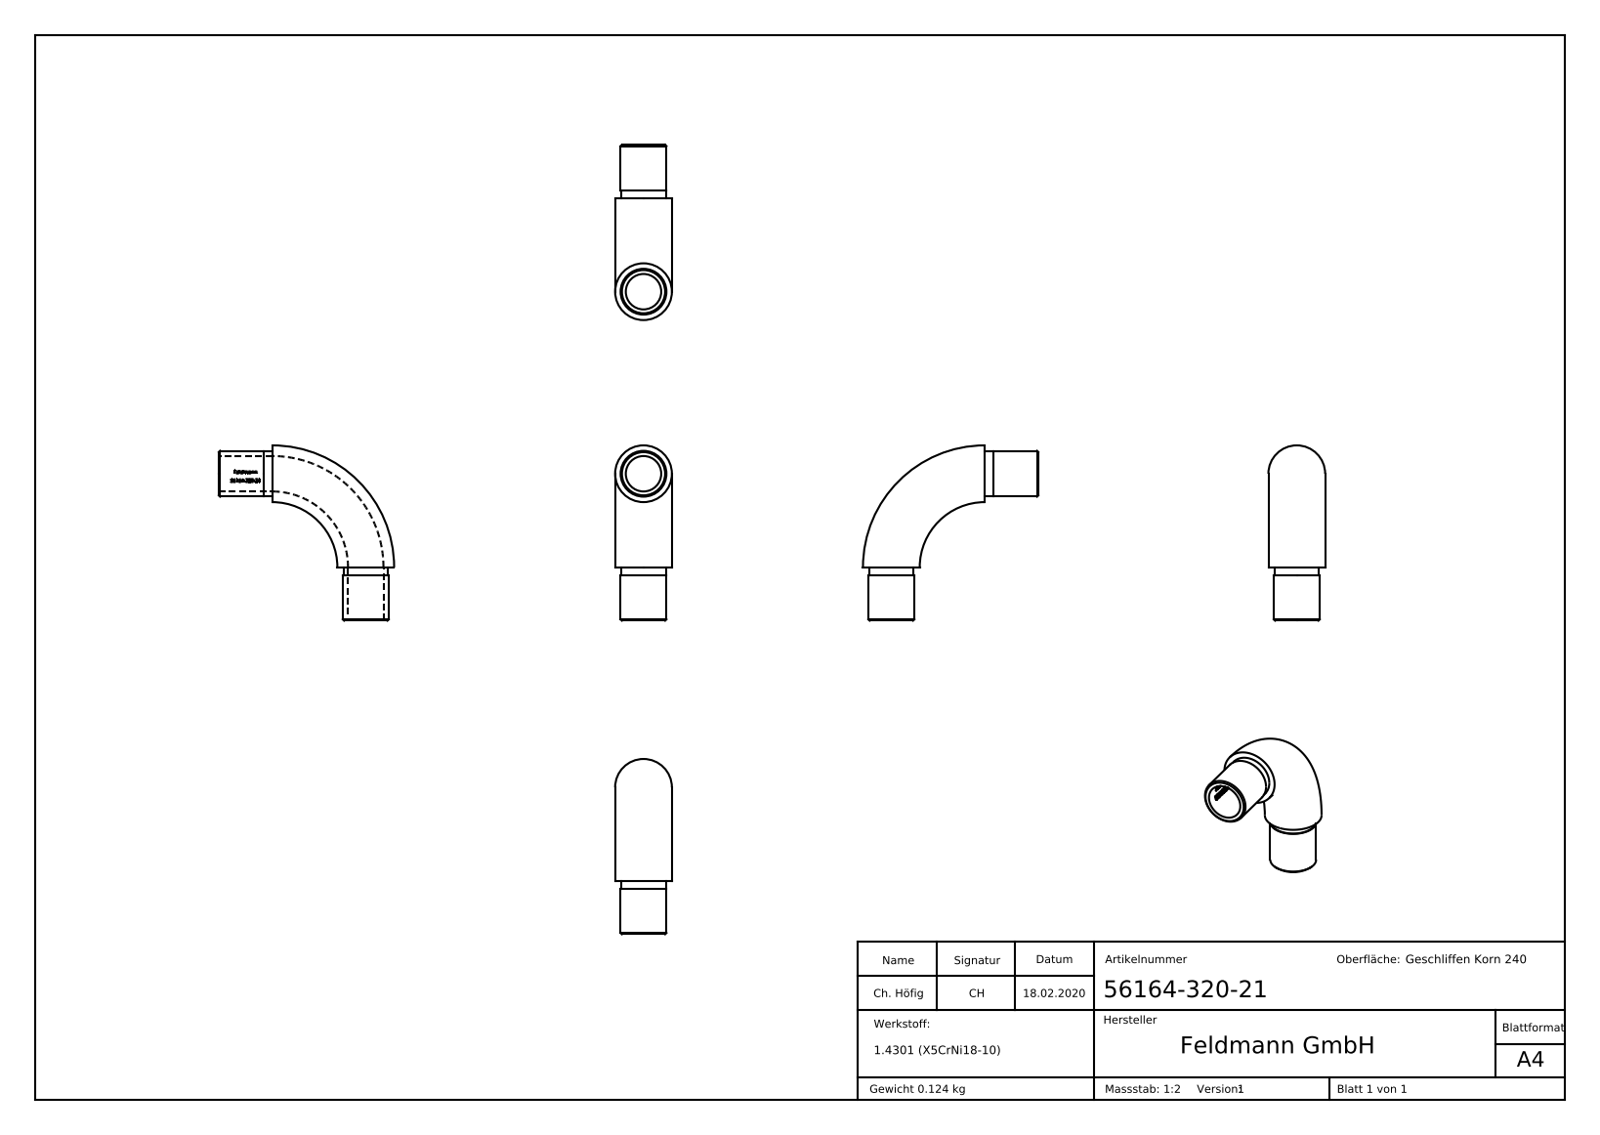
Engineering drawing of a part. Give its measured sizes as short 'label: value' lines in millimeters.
name: 56164-320-21
written by: SolidWorks 2015 (CONFIG_CONTROL_DESIGN)
unit: mm
bodies: 1 solid, 266 faces (120 planar, 33 cylindrical, 113 other)
size: 65.8 × 65.8 × 21.3
volume: 15 662 mm³; area: 10 283 mm²
holes: 2× ⌀13.3
bosses: 2× ⌀17.2, 2× ⌀16.8
rounds: 1× R6.75
face distances: 20, 17, 3, 1.32, 1.19, 0.44, 8.35, 51.95, 34.95, 31.95
